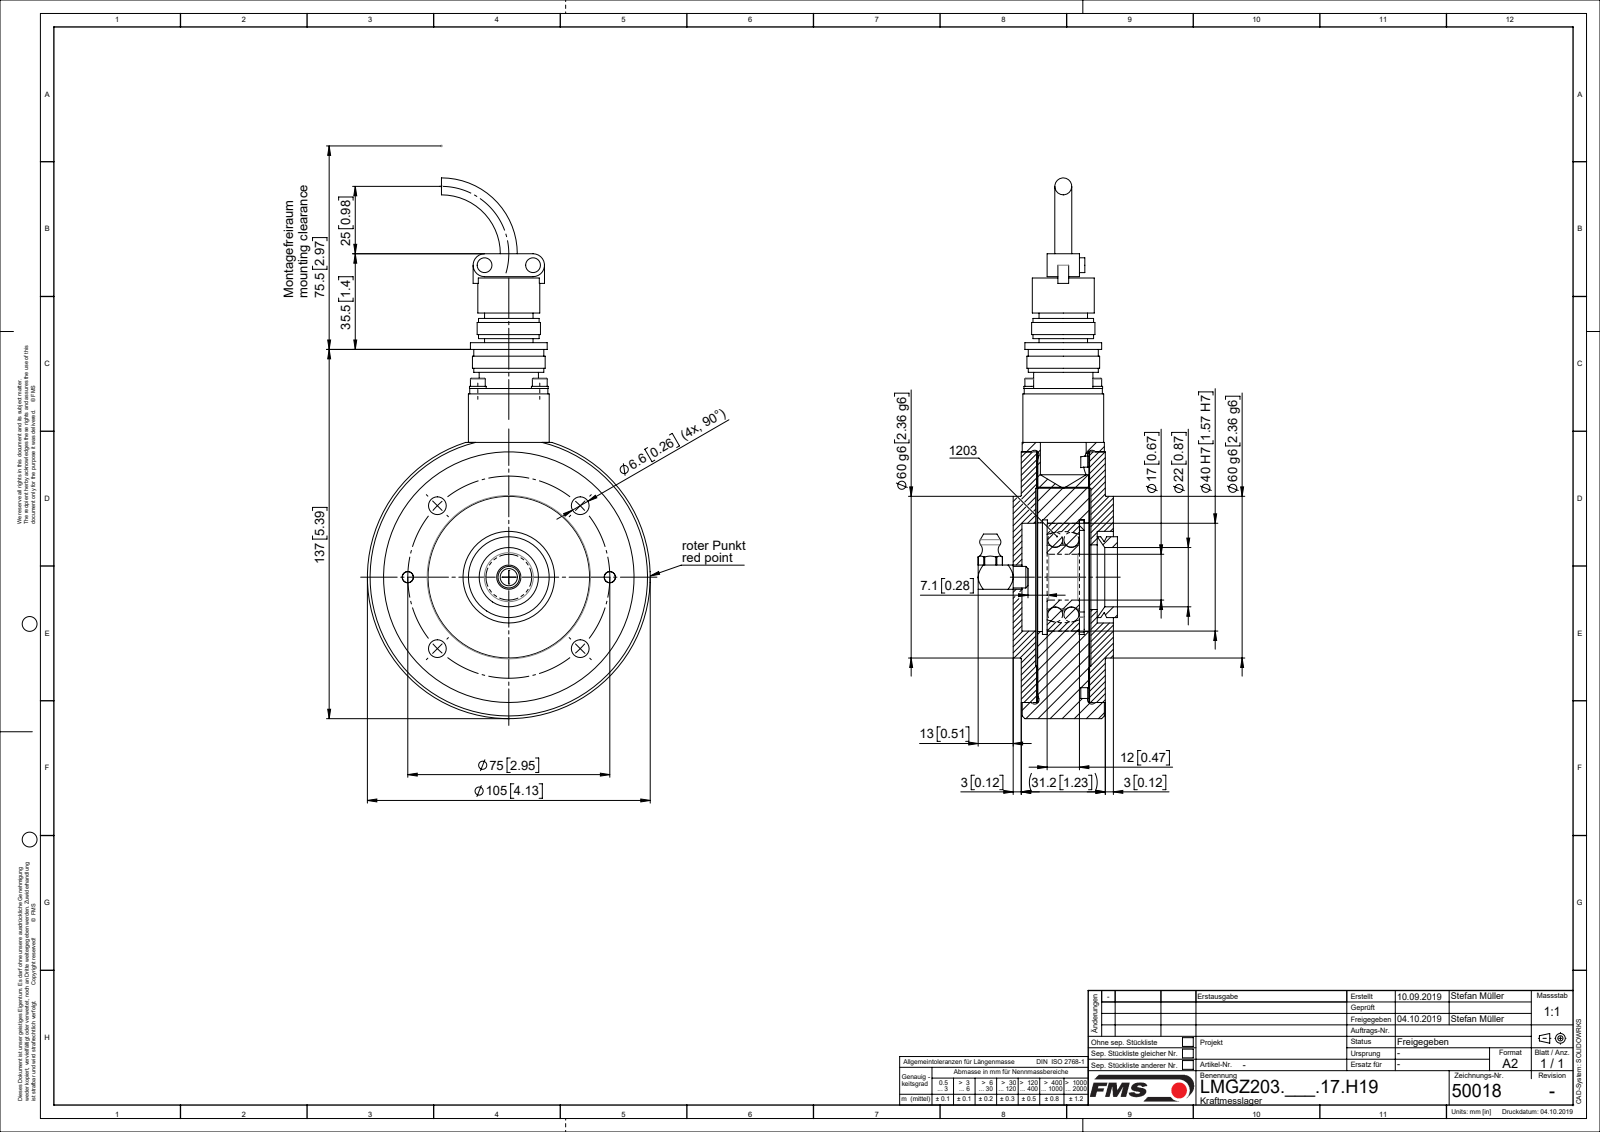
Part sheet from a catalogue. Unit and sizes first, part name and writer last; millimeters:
Units: millimetres
Overall size (bounding box): 200.65 × 105 × 51.7
Round holes (diameter × count): ⌀2.6 ×4, ⌀3.2 ×4, ⌀3.4 ×4, ⌀6.6 ×4, ⌀4 ×2, ⌀5.3 ×2, ⌀5.5 ×2, ⌀10 ×2, ⌀8.68 ×1, ⌀17 ×1, ⌀22 ×1, ⌀23 ×1
Round bosses / shafts (diameter × count): ⌀5.5 ×6, ⌀6.2 ×4, ⌀3 ×4, ⌀2.5 ×4, ⌀8 ×3, ⌀5 ×2, ⌀105 ×1, ⌀93 ×1
Partial cylindrical surfaces — rounded edges, fillets, slot ends (radius × count): R4.25 ×2, R2 ×1
Main face-to-face distances: 19.25, 19, 5.85, 25.1, 6.1, 25.35, 19.5, 20, 3, 0.5
Hole centre spacings: 37.5, 16.26, 23, 28.7, 53.04, 69.3, 32.53, 75.01
Volume: 288 254 mm³ · Surface area: 104 783 mm²
Bodies: 21 solids, 409 faces (124 planar, 231 cylindrical, 54 other)
Part name (STEP PRODUCT): L50018; L4795904; L47958; L49601 (+8 more)
STEP written by: Mechanical Desktop 2007 (CONFIG_CONTROL_DESIGN)
